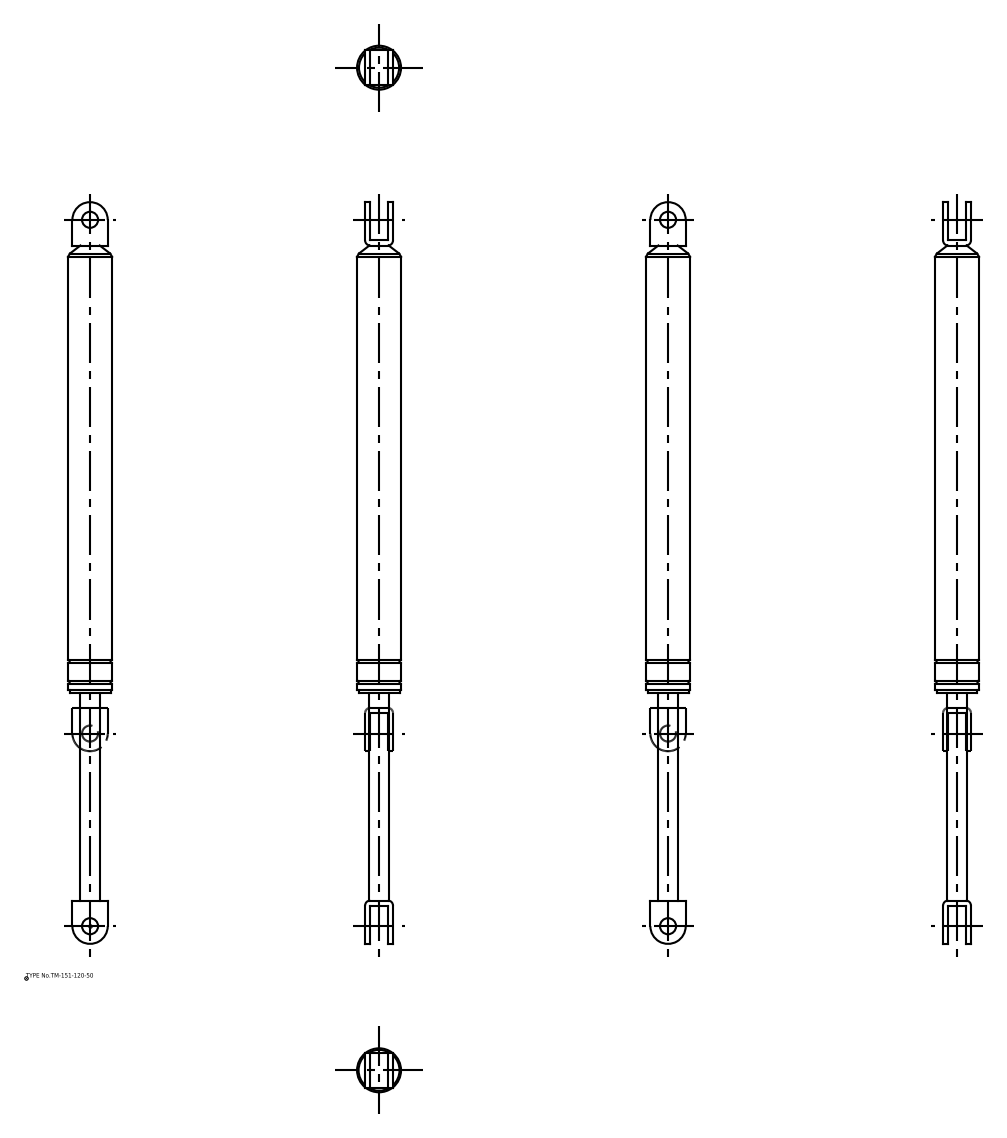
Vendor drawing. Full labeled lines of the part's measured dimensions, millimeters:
Part name (STEP PRODUCT): TM_151_120_50; TM_151_120_50_div
STEP written by: spGate 16.7.1 (AUTOMOTIVE_DESIGN)
Units: millimetres
Bodies: 2 solids, 64 faces (22 planar, 32 cylindrical, 10 other)
Overall size (bounding box): 462 × 28.2 × 28.2
Volume: 186 044 mm³ · Surface area: 35 864 mm²
Round holes (diameter × count): ⌀10 ×2
Round bosses / shafts (diameter × count): ⌀28.2 ×1, ⌀27.4 ×1, ⌀25.5 ×1, ⌀12.5 ×1
Partial cylindrical surfaces — rounded edges, fillets, slot ends (radius × count): R3.2 ×4, R11 ×2
Main face-to-face distances: 3.2, 14.2, 17.4, 11, 22, 411.2, 132.2, 414.4, 282.2, 279
Hole centre spacings: 440
